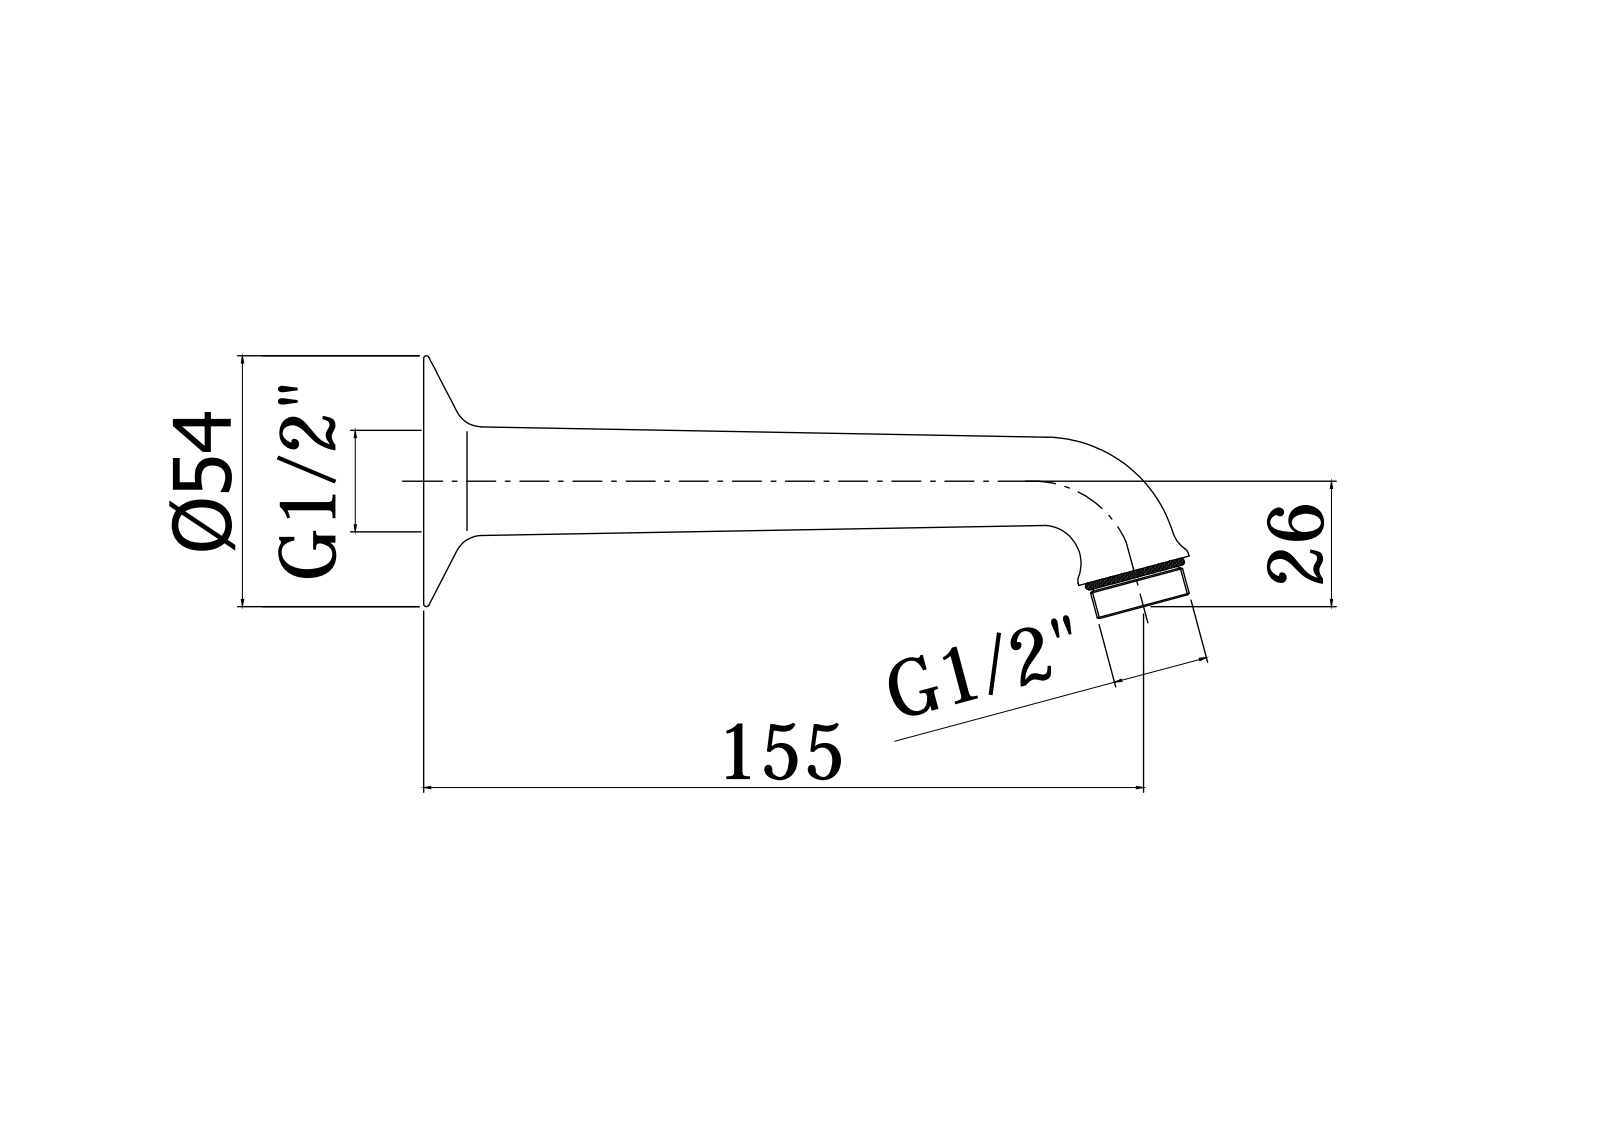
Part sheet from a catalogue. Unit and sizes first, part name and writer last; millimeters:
Units: millimetres
Overall size (bounding box): 165.23 × 54.53 × 54
Round holes (diameter × count): ⌀14.6 ×1
Round bosses / shafts (diameter × count): ⌀54 ×1, ⌀24.5 ×1, ⌀21 ×1, ⌀18.5 ×1
Main face-to-face distances: 8, 6, 2
Volume: 25 171 mm³ · Surface area: 24 569 mm²
Bodies: 2 solids, 56 faces (4 planar, 10 cylindrical, 42 other)
Part name (STEP PRODUCT): ZSOF015CR
STEP written by: CREO PARAMETRIC BY PTC INC, 2020044 (CONFIG_CONTROL_DESIGN)
